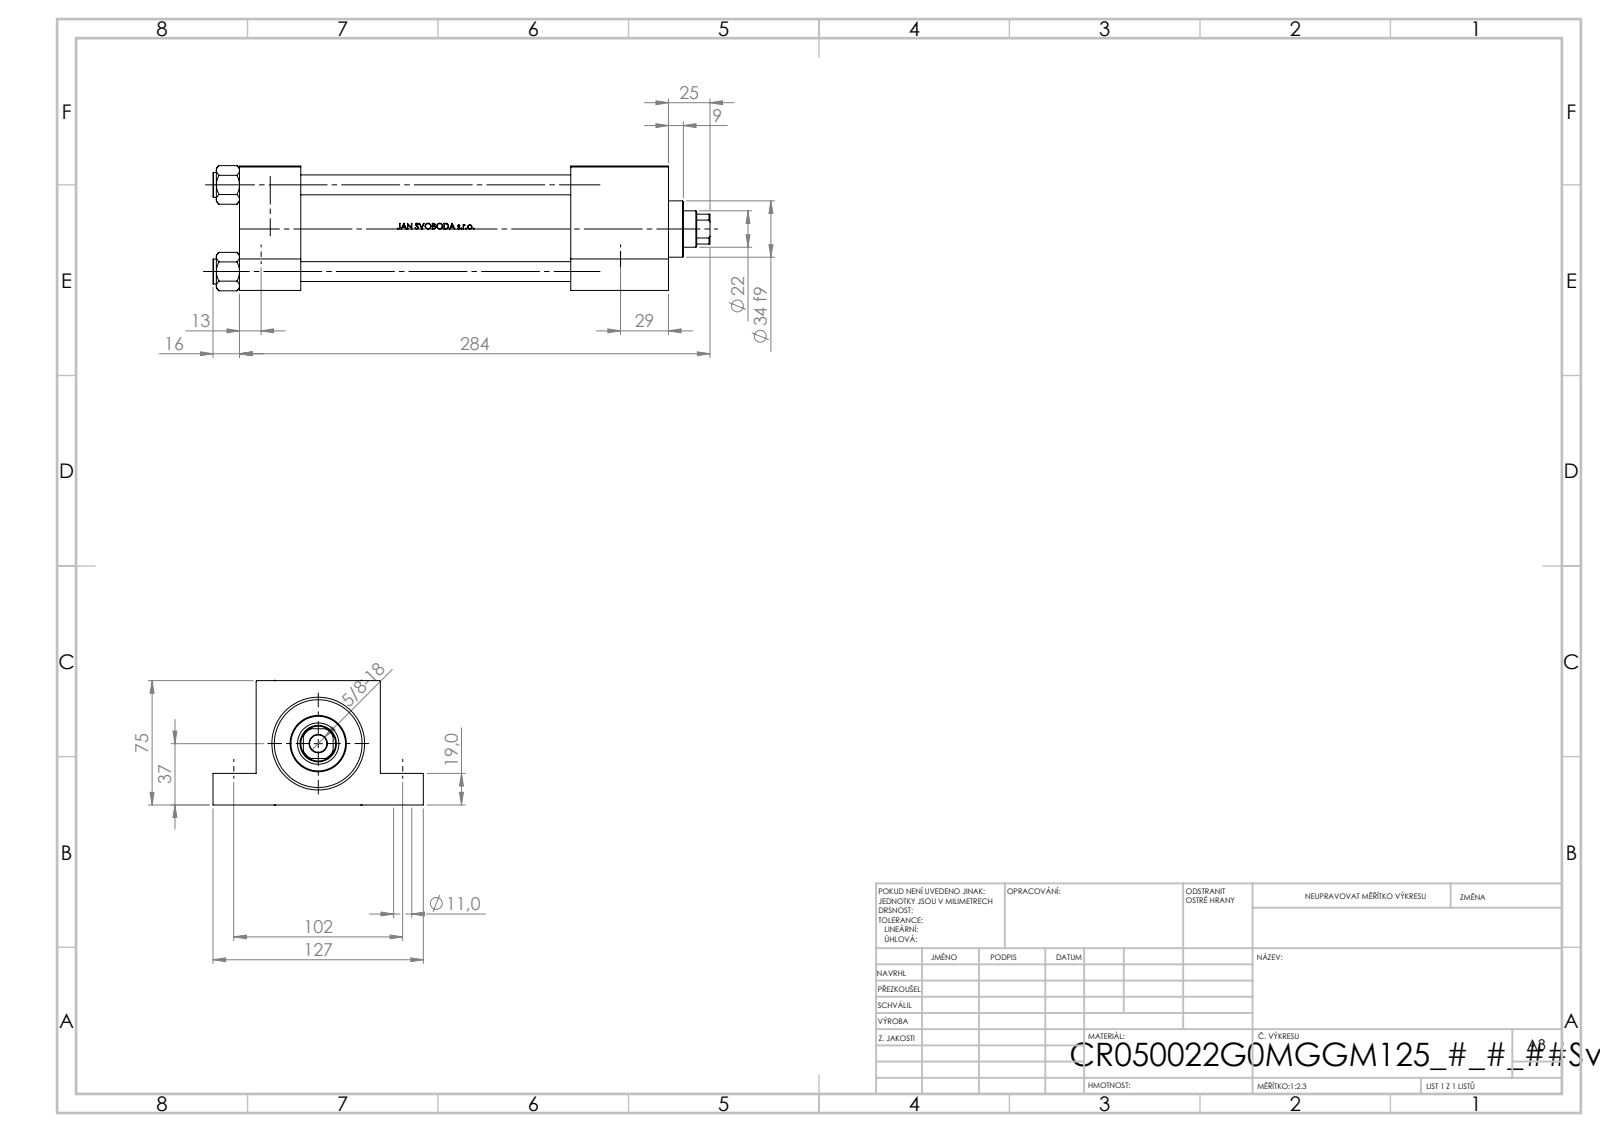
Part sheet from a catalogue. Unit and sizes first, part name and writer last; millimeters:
Units: millimetres
Overall size (bounding box): 300 × 127 × 75.54
Round holes (diameter × count): ⌀11 ×4, ⌀12 ×4, ⌀7 ×2, ⌀20.96 ×2, ⌀30 ×2, ⌀10.5 ×1, ⌀22 ×1, ⌀25 ×1, ⌀41 ×1, ⌀50 ×1, ⌀53 ×1
Round bosses / shafts (diameter × count): ⌀15 ×4, ⌀56 ×1, ⌀34 ×1
Partial cylindrical surfaces — rounded edges, fillets, slot ends (radius × count): R10.5 ×1
Main face-to-face distances: 75, 37, 259, 222, 19, 56, 200, 163, 59, 26
Hole centre spacings: 52.3, 36.63, 37.34, 51.3, 52.63, 73.96, 102, 210.28
Volume: 895 617 mm³ · Surface area: 217 421 mm²
Bodies: 11 solids, 1088 faces (432 planar, 124 cylindrical, 532 other)
Part name (STEP PRODUCT): V215CR_G_TYCINKA; NUT_M5_G; V215CR_G_Body; V215_VC_A (+1 more)
STEP written by: SolidWorks 2019 (CONFIG_CONTROL_DESIGN)
